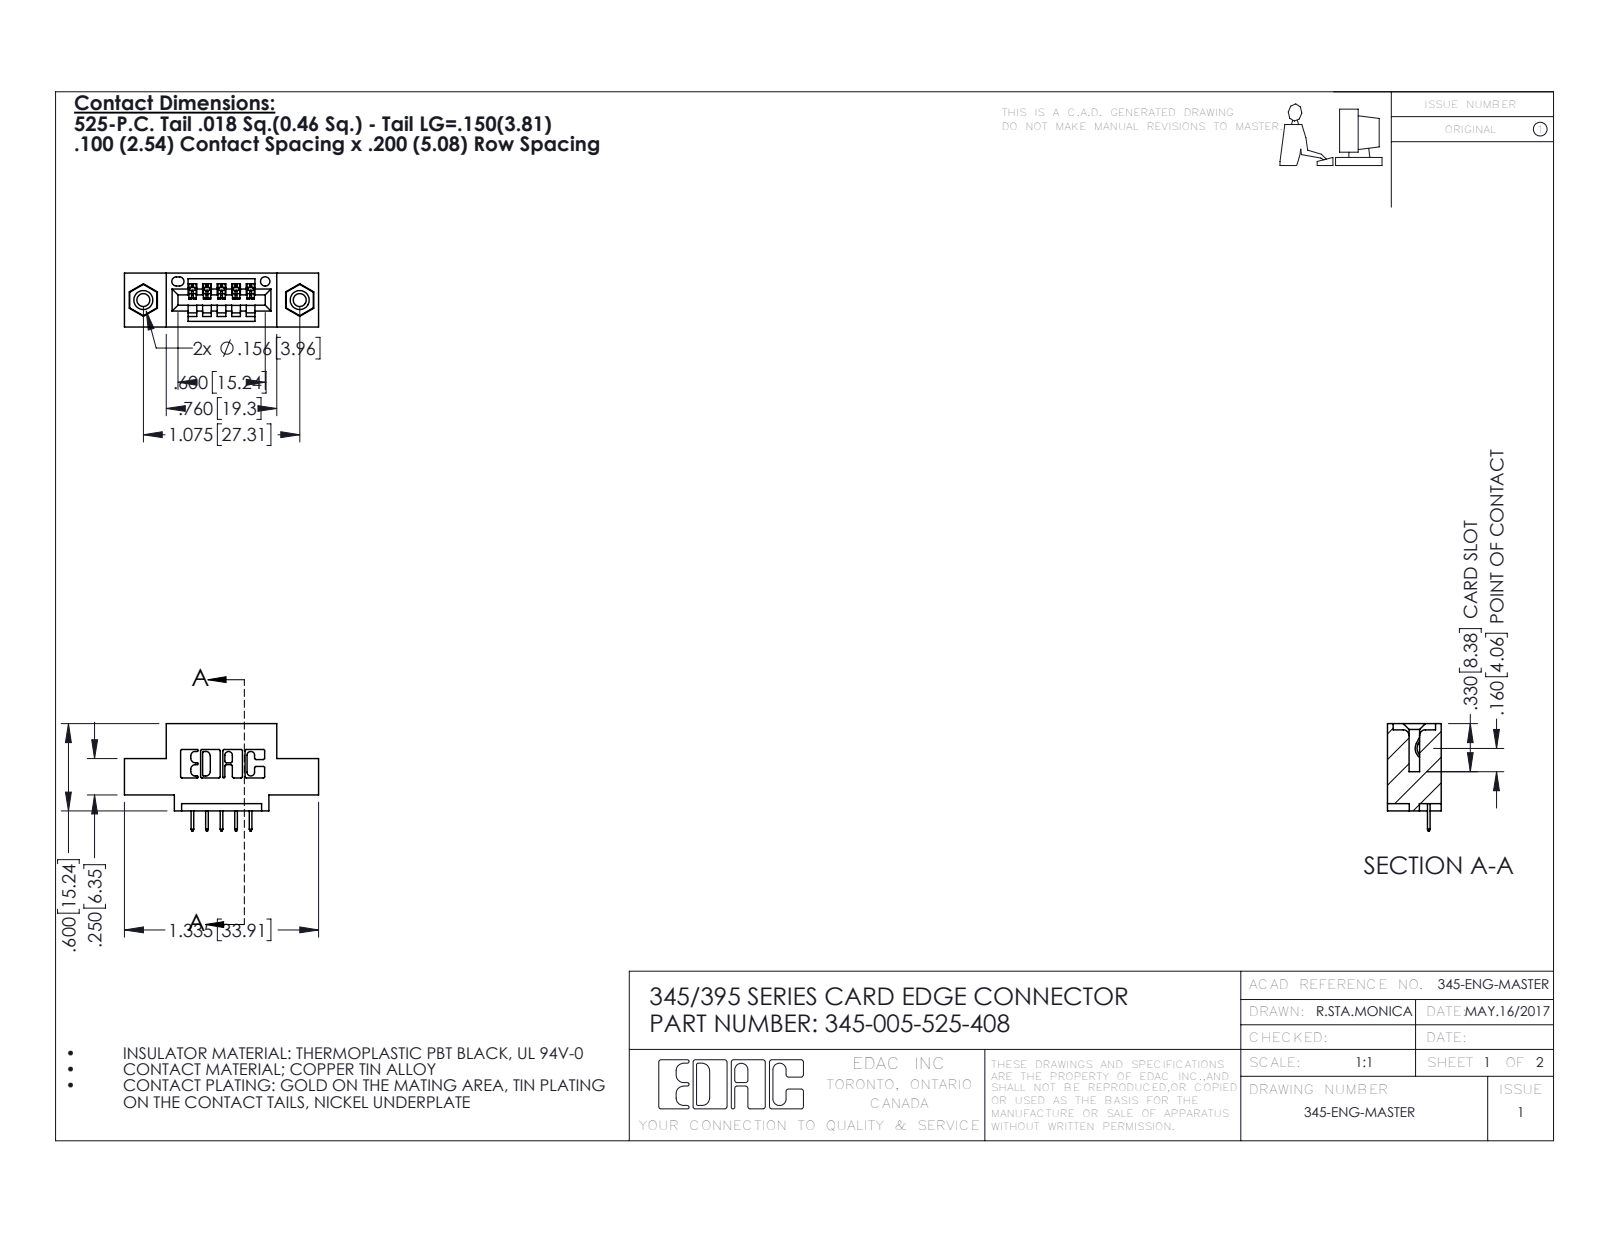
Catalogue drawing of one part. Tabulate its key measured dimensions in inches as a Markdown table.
| quantity | value |
| --- | --- |
| part name | 345-292-001_345-293-125; 345-250-001_345-250-003-102; 345 Part_0.110 Offset - 0.156 Dia-TI; 345-005-525-408 |
| STEP written by | SolidWorks 2020 (CONFIG_CONTROL_DESIGN) |
| units | inches |
| bodies | 8 solids, 500 faces (346 planar, 138 cylindrical, 16 other) |
| overall size | 1.335 × 0.737 × 0.37 |
| volume | 0.172 in³ |
| surface area | 5.075 in² |
| round holes (diameter × count) | 0.089 × 2, 0.125 × 2, 0.156 × 2, 0.064 × 1 |
| round bosses / shafts (diameter × count) | 0.155 × 2 |
| partial cylindrical surfaces (radius × count) | 0.01 × 22, 0.006 × 10, 0.007 × 6, 0.031 × 6, 0.026 × 3, 0.031 × 2, 0.04 × 2, 0.014 × 1 |
| main face-to-face distances | 0.2, 0.37, 0.1, 0.072, 0.298, 0.025, 0.25, 0.06, 0.16, 0.04 |
| hole center spacings | 0.27, 0.847, 1.075 |
